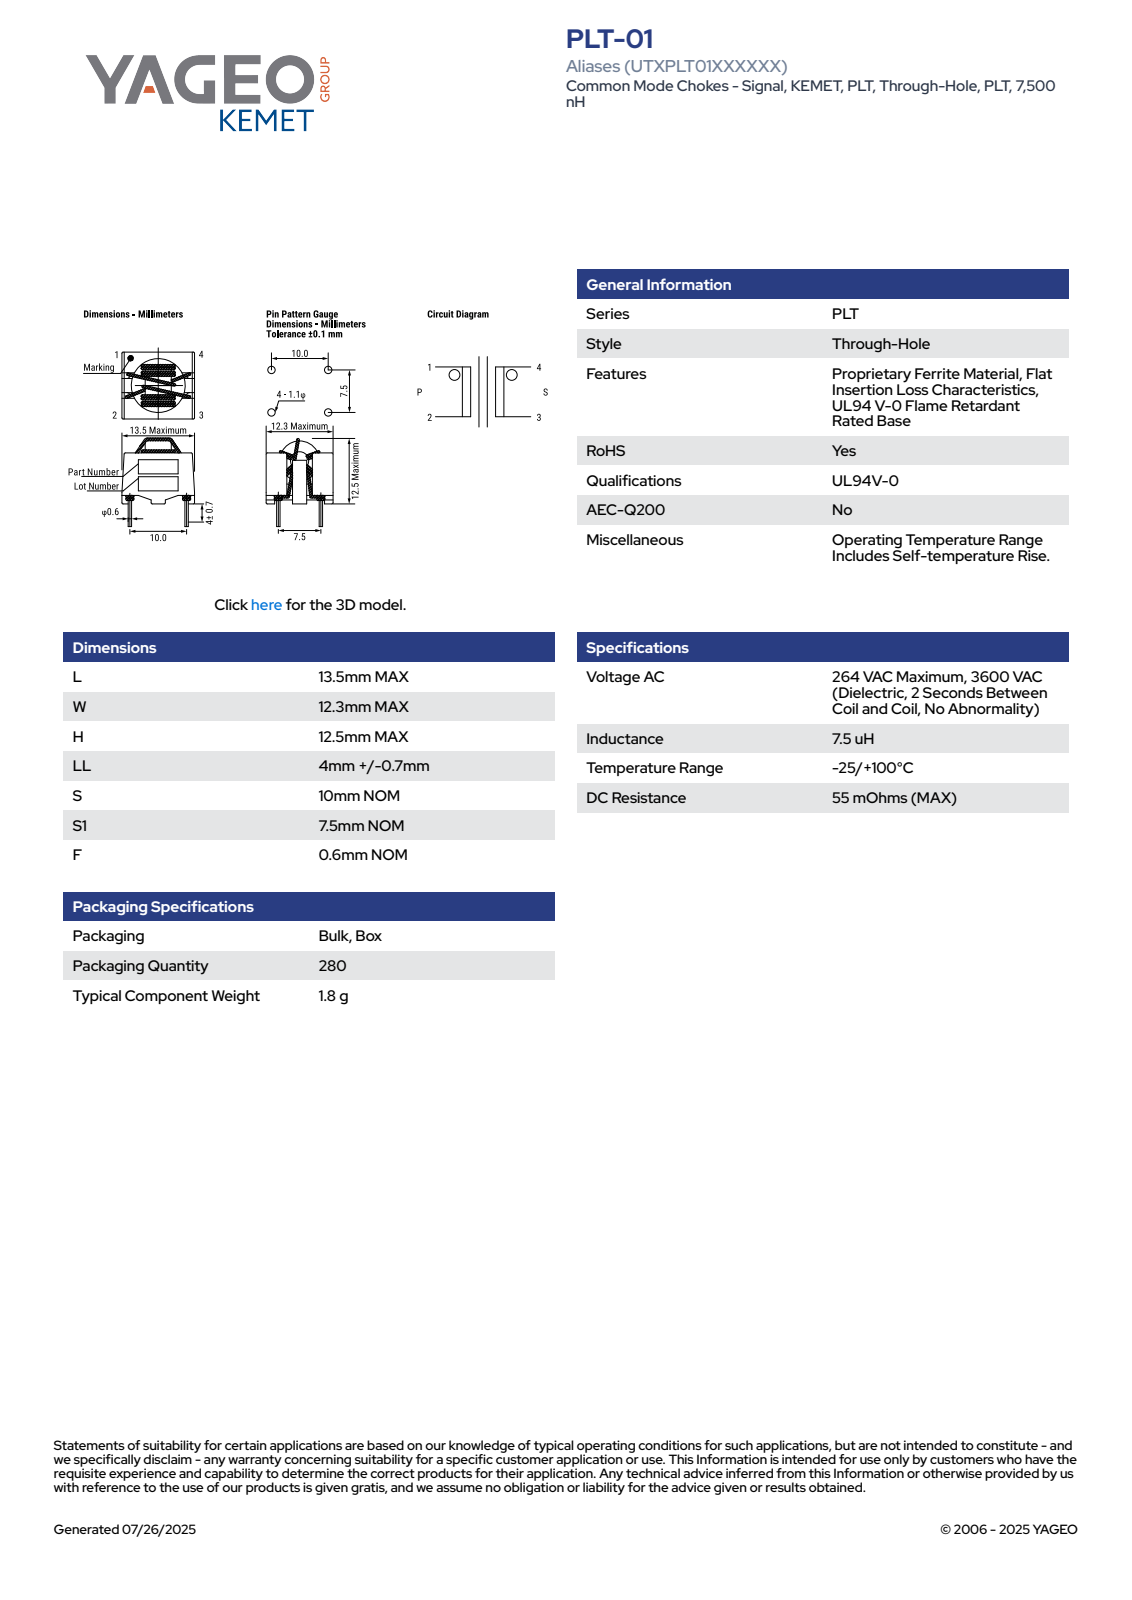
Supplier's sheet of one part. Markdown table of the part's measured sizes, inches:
| quantity | value |
| --- | --- |
| part name | PT_KPLT01_L13.5W12.3H12.5LL4.7S10 |
| STEP written by | SolidWorks 2014 (AUTOMOTIVE_DESIGN) |
| units | inches |
| bodies | 2 solids, 457 faces (167 planar, 176 cylindrical, 114 other) |
| overall size | 0.677 × 0.531 × 0.484 |
| volume | 0.065 in³ |
| surface area | 2.289 in² |
| round holes (diameter × count) | 0.145 × 1, 0.418 × 1 |
| round bosses / shafts (diameter × count) | 0.024 × 4, 0.283 × 1 |
| partial cylindrical surfaces (radius × count) | 0.009 × 113, 0.004 × 14 |
| main face-to-face distances | 0.484, 0.079, 0.098, 0.335, 0.256, 0.207, 0.277, 0.18, 0.305, 0.028 |
